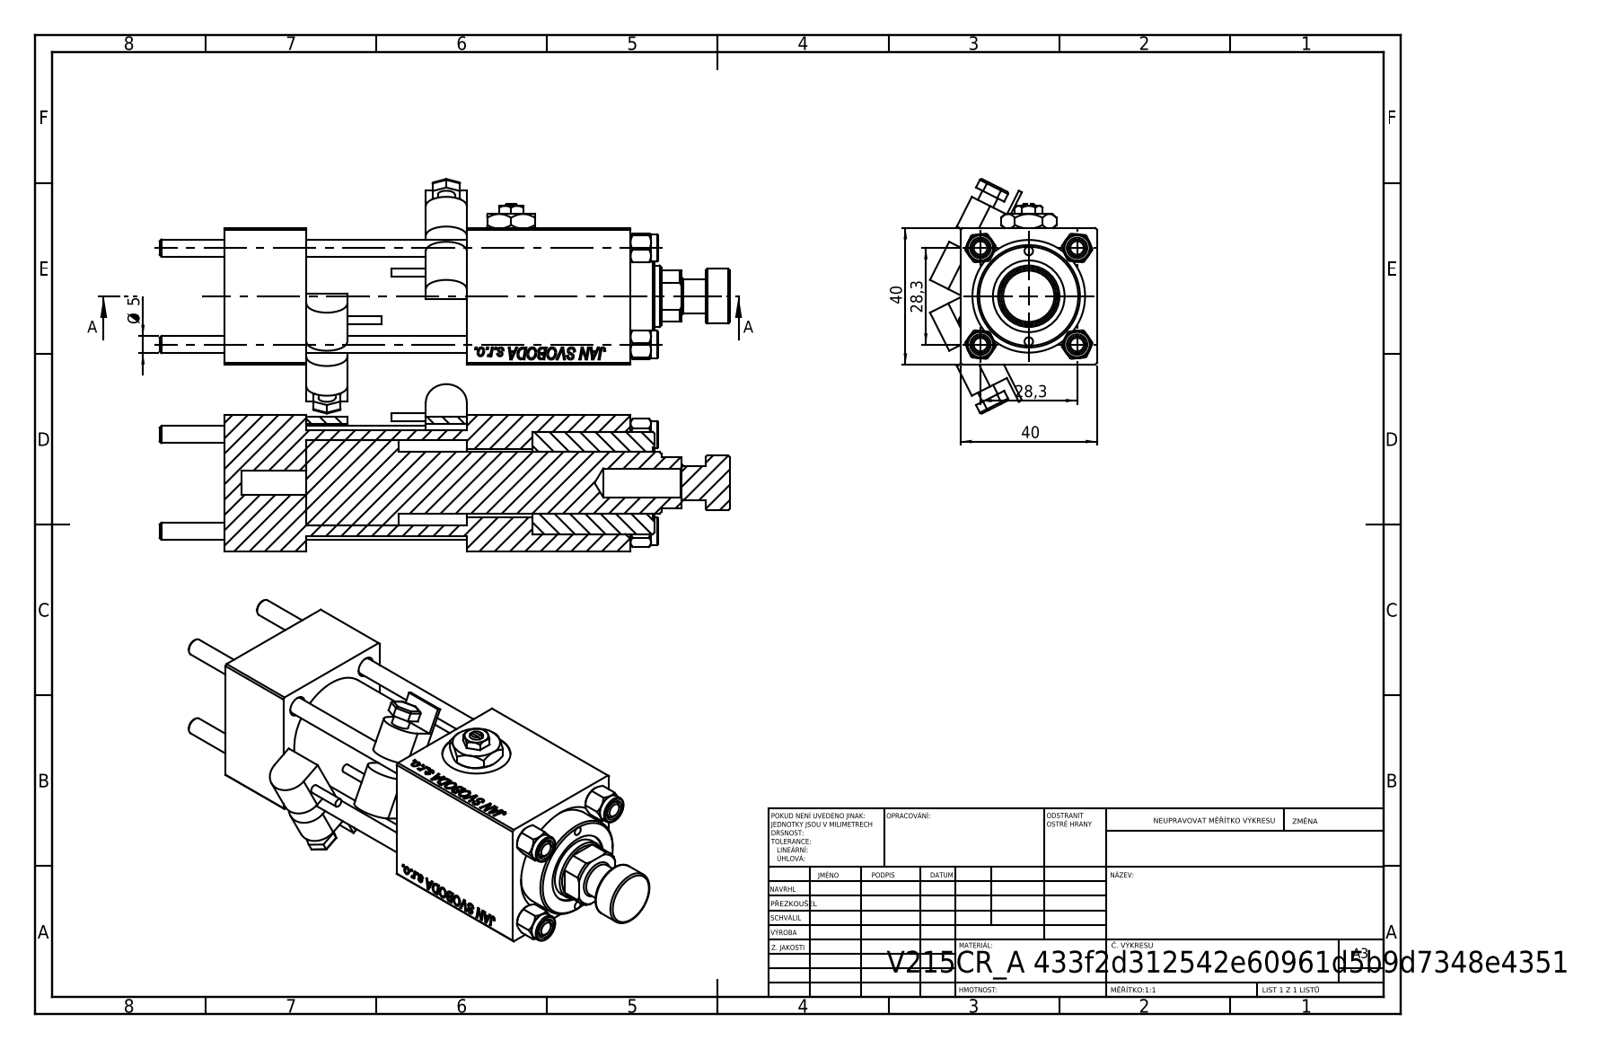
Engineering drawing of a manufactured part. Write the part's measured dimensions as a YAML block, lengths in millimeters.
part_name: "V215CR_BODY_A; CR025_012_A_0_G_A_G_M_020_+#_##_TYCINKA; V215CR_ROD_END_W; V215CR_VCP (+4 more)"
step_written_by: "SolidWorks 2019 (CONFIG_CONTROL_DESIGN)"
units: millimeters
bodies: {solids: 15, faces: 1259, planar: 581, cylindrical: 116, other: 562}
overall_size: [167, 68.71, 48.93]
volume: 160520
surface_area: 67206
round_holes:
  - {diameter: 5, count: 4}
  - {diameter: 20, count: 3}
  - {diameter: 2.5, count: 2}
  - {diameter: 7, count: 2}
  - {diameter: 13.16, count: 2}
  - {diameter: 8.5, count: 1}
  - {diameter: 18, count: 1}
  - {diameter: 21, count: 1}
  - {diameter: 25, count: 1}
  - {diameter: 30, count: 1}
round_bosses_or_shafts:
  - {diameter: 8, count: 4}
  - {diameter: 5, count: 2}
  - {diameter: 2.5, count: 2}
  - {diameter: 31, count: 1}
  - {diameter: 16, count: 1}
  - {diameter: 10, count: 1}
partial_cylinders:
  - {radius: 0.5, count: 12}
  - {radius: 6, count: 4}
  - {radius: 8.5, count: 1}
face_to_face_distances: [40, 24, 71, 47, 90.3, 66.3, 19.3, 8, 119, 95]
hole_center_spacings: [14.18, 20.01, 28.3, 30.84, 13.25, 40.02, 26.5, 72]
